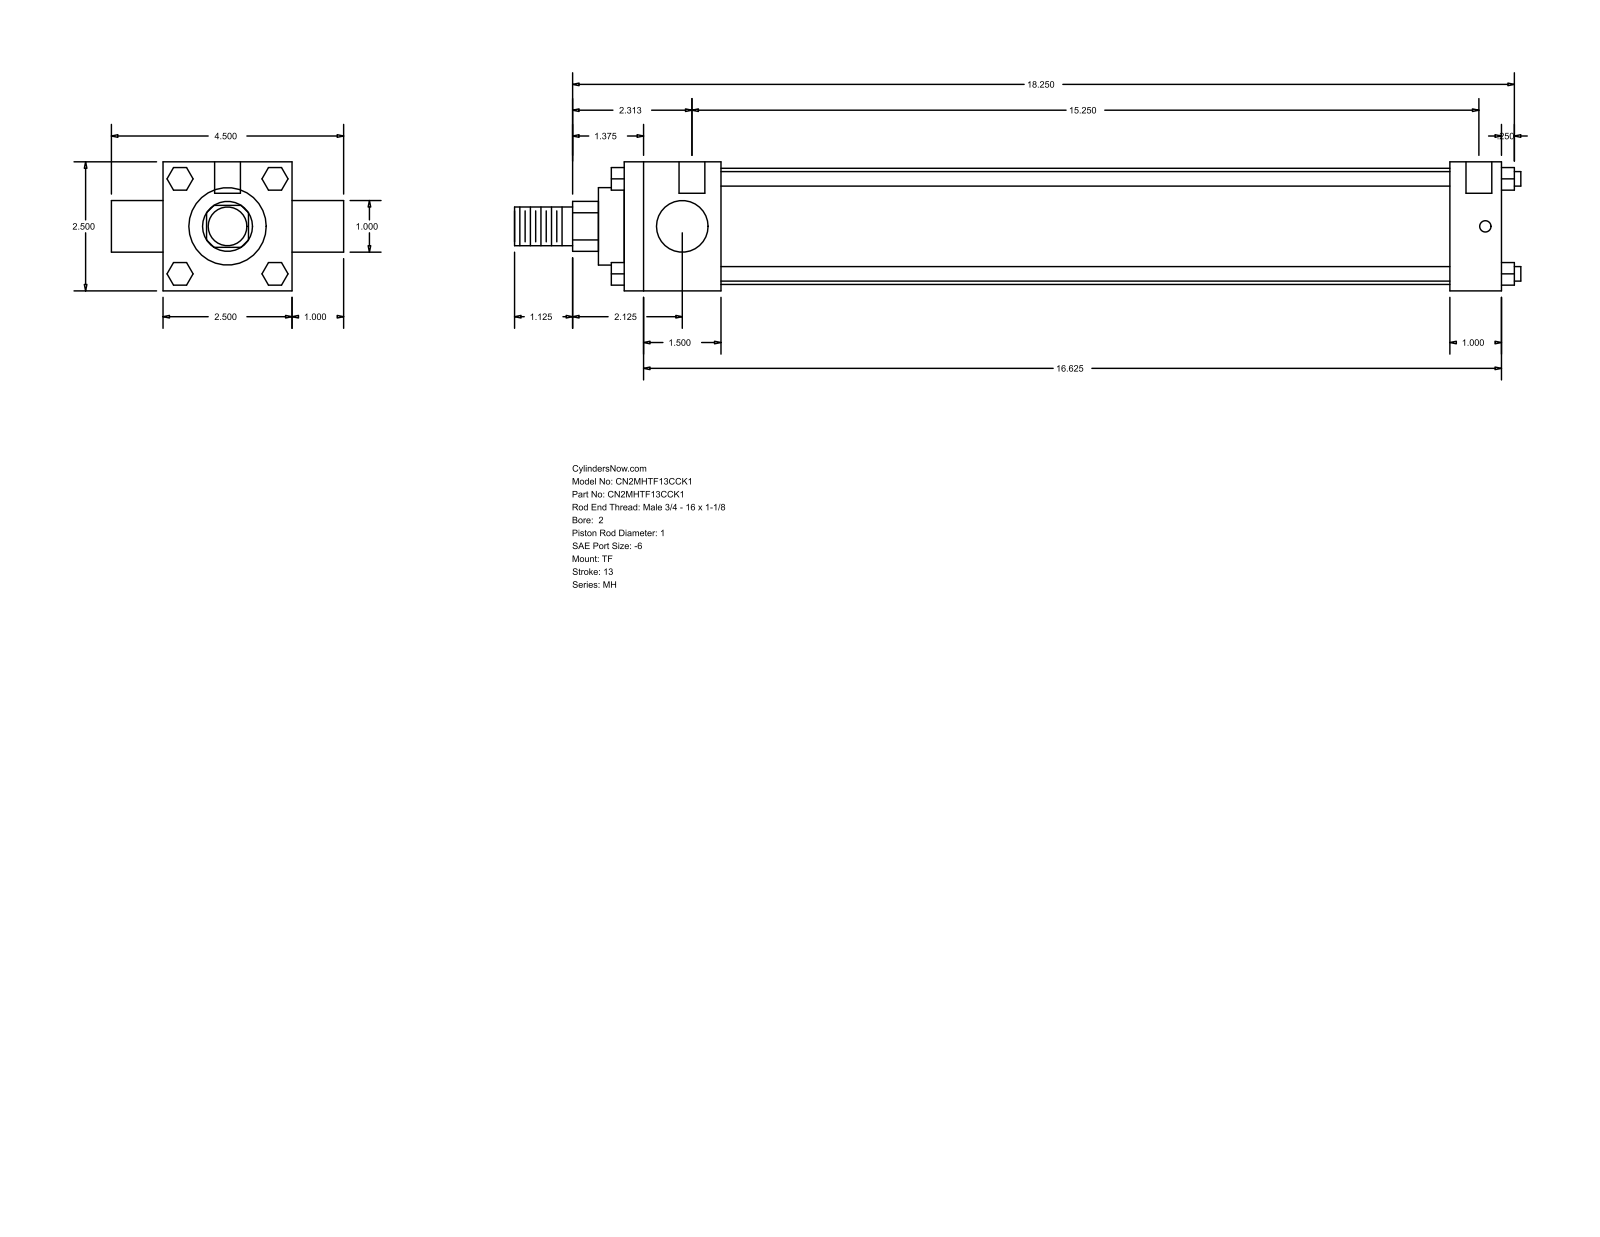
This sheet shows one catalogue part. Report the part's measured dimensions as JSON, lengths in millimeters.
{"part_name": "MH_TF__0200_1", "step_written_by": "GSSL Pune (CONFIG_CONTROL_DESIGN)", "units": "millimeters", "bodies": {"solids": 0, "faces": 120, "planar": 92, "cylindrical": 28, "other": 0}, "overall_size": [495.3, 114.3, 63.5], "round_holes": [[5.56, 3], [12.7, 2]], "round_bosses_or_shafts": [[7.14, 4], [25.4, 2], [57.15, 1], [38.1, 1], [19.05, 1]], "partial_cylinders_radius": [[12.29, 1]], "face_to_face_distances": [63.5, 431.8, 25.4, 47.63, 406.4, 358.77, 384.17, 88.9, 444.5, 6.35], "hole_center_spacings": [3.17, 4.76, 387.35, 390.52, 392.11, 395.28]}
